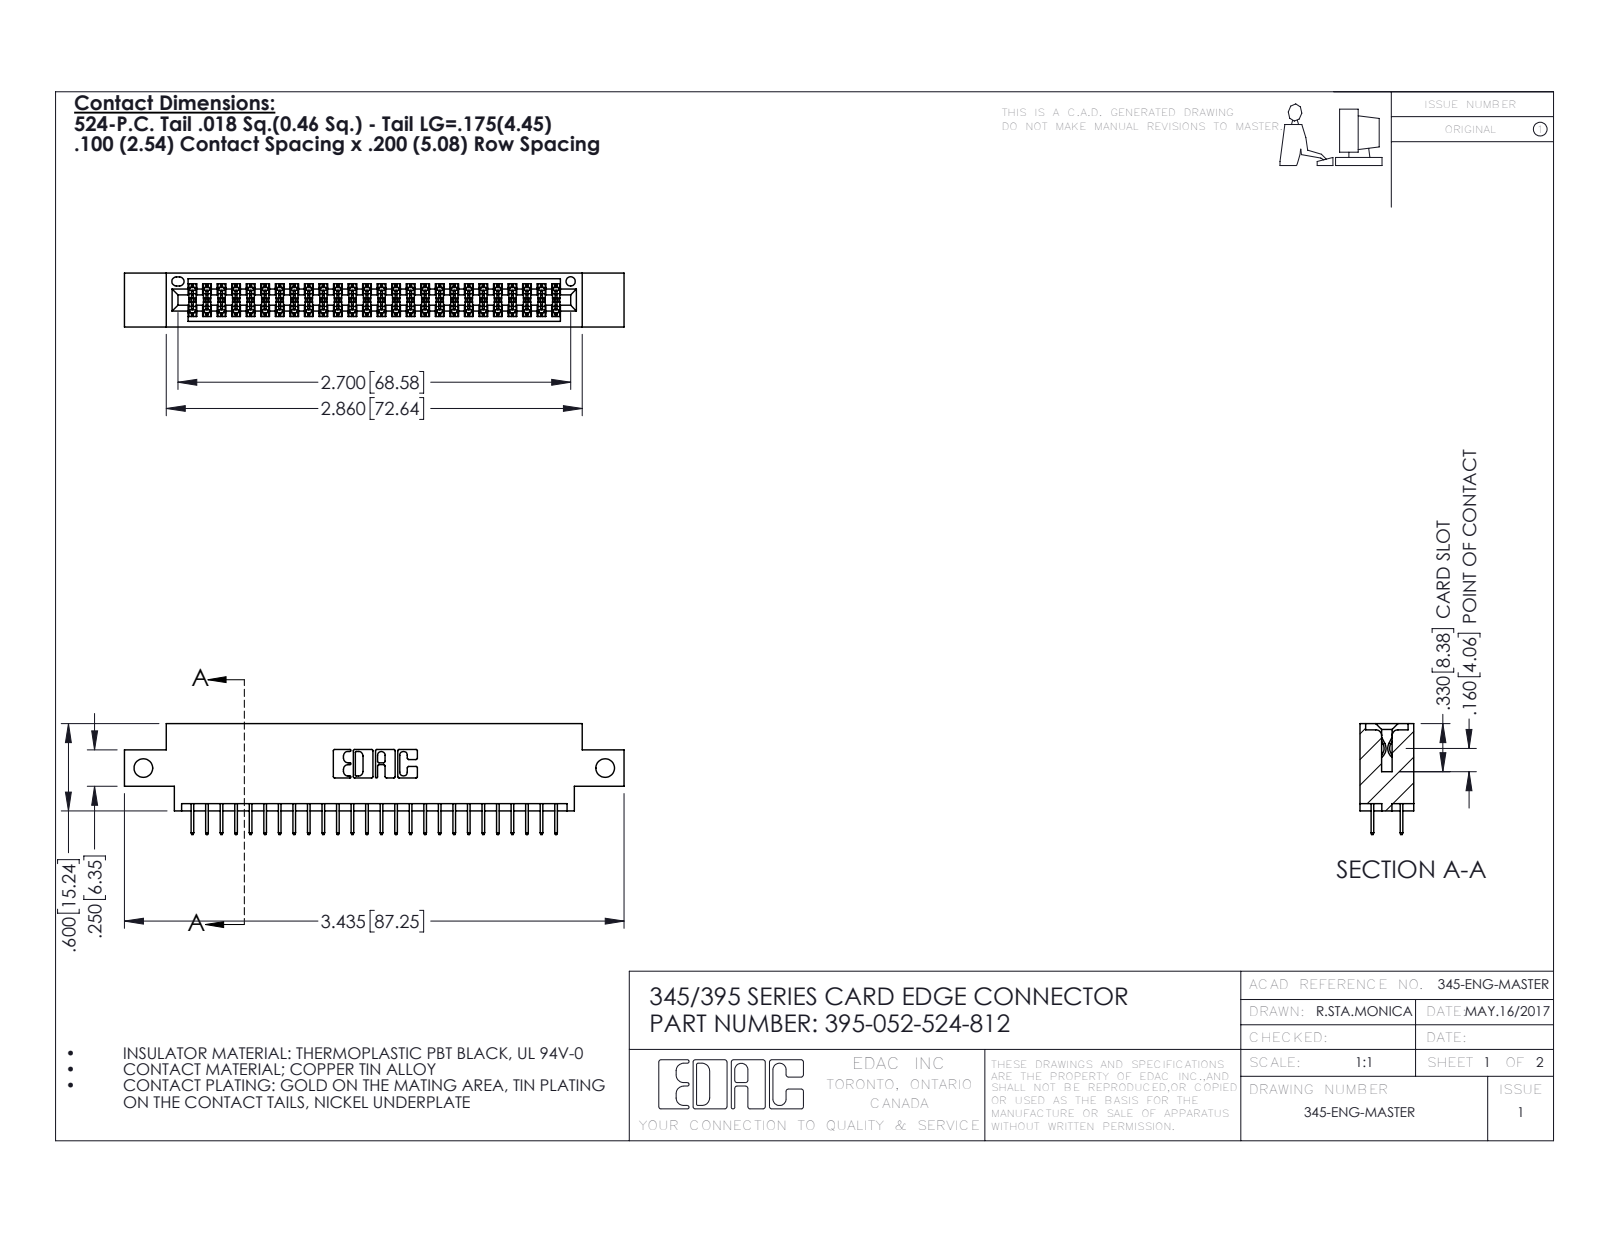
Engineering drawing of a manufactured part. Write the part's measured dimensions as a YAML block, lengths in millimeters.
part_name: "345-292-001_345-293-124; 395-052-524-812; 345 Part_0.170 Offset - Side Mount"
step_written_by: "SolidWorks 2016 (CONFIG_CONTROL_DESIGN)"
units: millimeters
bodies: {solids: 53, faces: 2938, planar: 2112, cylindrical: 826, other: 0}
overall_size: [87.2, 19.4, 9.4]
volume: 8050
surface_area: 11390
round_holes:
  - {diameter: 3.3, count: 2}
  - {diameter: 1.6, count: 1}
partial_cylinders:
  - {radius: 0.2, count: 78}
  - {radius: 0.3, count: 22}
  - {radius: 0.2, count: 6}
  - {radius: 0.8, count: 6}
  - {radius: 0.7, count: 3}
  - {radius: 0.4, count: 2}
  - {radius: 0.5, count: 2}
  - {radius: 0.6, count: 2}
face_to_face_distances: [1.8, 7.6, 9.4, 5.1, 2.5, 6.9, 0.6, 5.7, 4.4, 1.8]
hole_center_spacings: [80.6]
